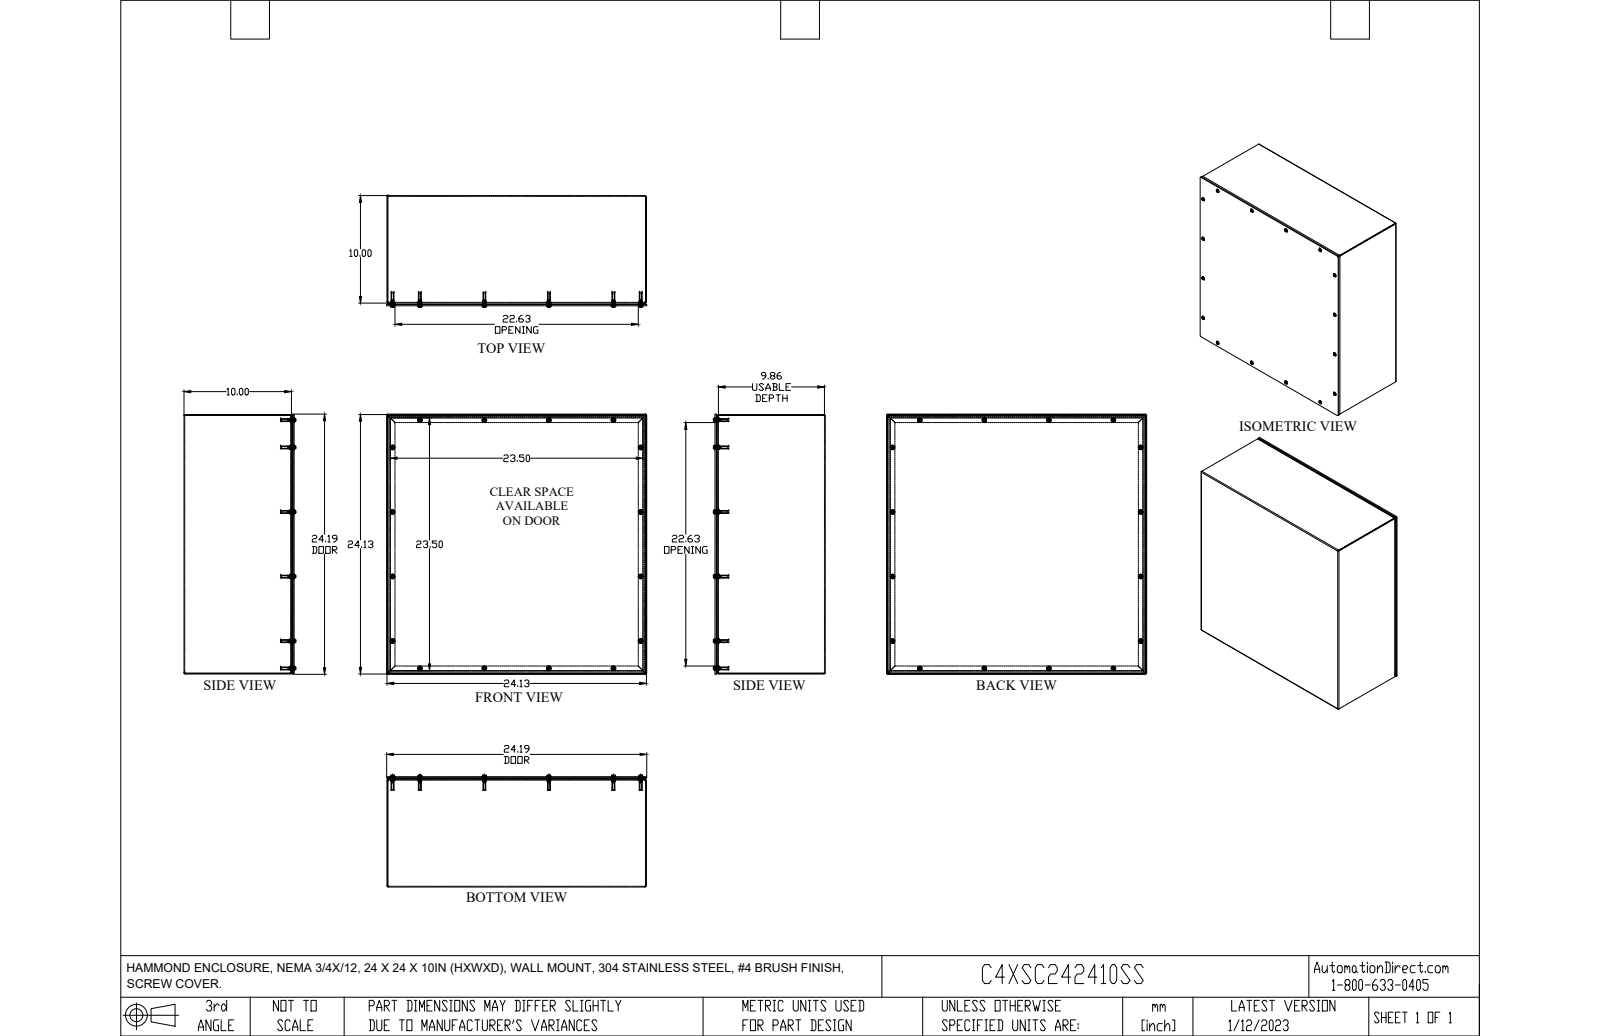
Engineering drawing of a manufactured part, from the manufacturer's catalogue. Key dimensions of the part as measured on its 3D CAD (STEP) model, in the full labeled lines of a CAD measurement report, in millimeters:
Part name (STEP PRODUCT): C3SC242410GY
STEP written by: SolidWorks 2021 (AUTOMOTIVE_DESIGN)
Units: millimetres
Bodies: 51 solids, 1476 faces (920 planar, 272 cylindrical, 284 other)
Overall size (bounding box): 614.4 × 614.4 × 264.2
Volume: 3 079 000 mm³ · Surface area: 2 924 000 mm²
Round holes (diameter × count): ⌀4 ×16, ⌀4.1 ×16, ⌀6.4 ×16
Round bosses / shafts (diameter × count): ⌀11.2 ×16, ⌀9.9 ×16, ⌀6.1 ×16, ⌀4.8 ×16, ⌀3.8 ×16, ⌀7 ×12, ⌀7 ×4
Partial cylindrical surfaces — rounded edges, fillets, slot ends (radius × count): R4.1 ×16, R1 ×8, R2.8 ×8, R3.2 ×8, R3.2 ×4, R9.5 ×4
Main face-to-face distances: 1.8, 3.2, 260.4, 257.2, 258.6, 255.4, 612.9, 611.1, 611.1, 609.3
Hole centre spacings: 152.4, 605.6, 226.2, 304.8, 374.8, 428.2, 525.6, 564.9
